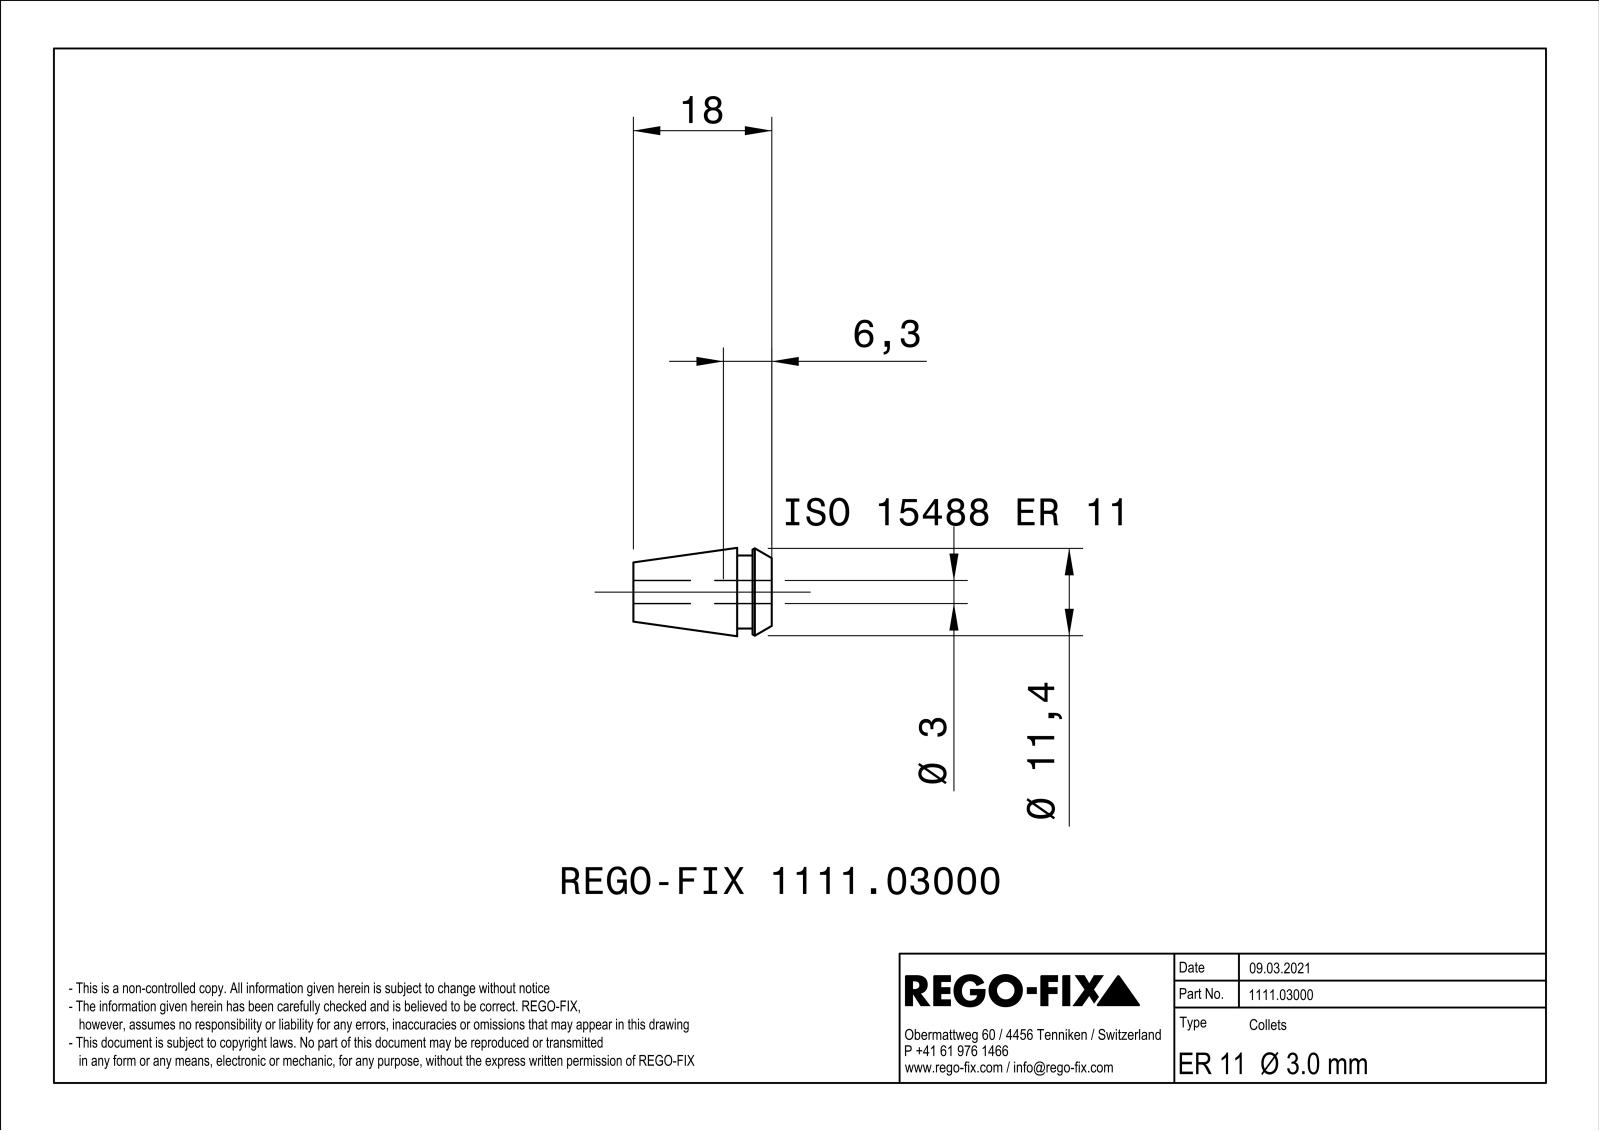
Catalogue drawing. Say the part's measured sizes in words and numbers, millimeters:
The part is named "NOCUT". Its 3-D file was written by "SIEMENS PLM Software Solid Edge ST10 (AUTOMOTIVE_DESIGN)". It is 1 solid with 157 faces: 66 planar, 37 cylindrical and 54 other. Overall it measures 18 by 11.5 by 11.49 millimeters. Its volume is 953 cubic millimeters and its surface area 1 881 square millimeters. Round holes: 1 of diameter 3. Round bosses or shafts: 1 of diameter 11.5, 1 of diameter 9.5. Partial cylindrical surfaces (rounded edges, fillets, slot ends): 12 of radius 25. The main face-to-face distances are 0.45, 0.46, 0.44, 18, 2.5, 15.5, 4.5, 2, 13.5, 4.
